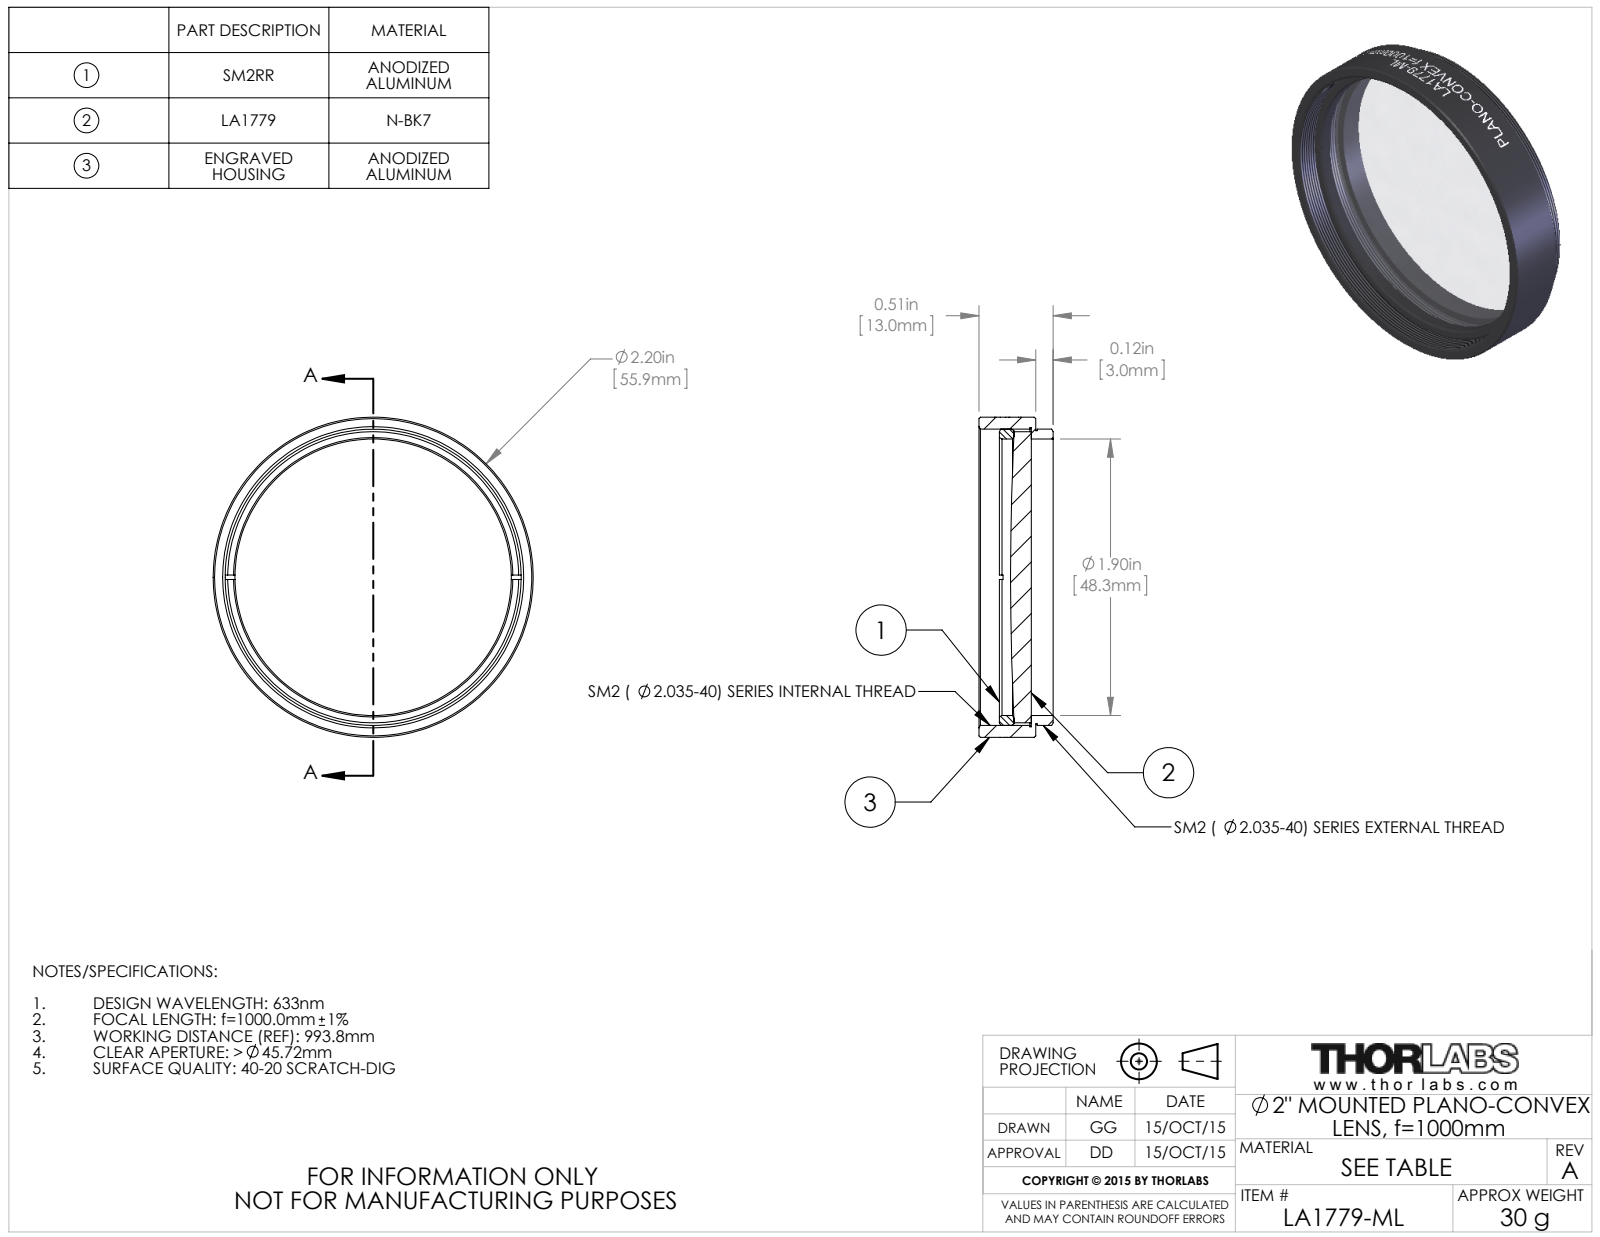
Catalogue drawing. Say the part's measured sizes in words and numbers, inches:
The part is named "TTN039630-E0W". Its 3-D file was written by "SolidWorks 2014 (CONFIG_CONTROL_DESIGN)". It is 3 solids with 110 faces: 16 planar, 74 cylindrical and 20 other. Overall it measures 2.2 by 2.2 by 0.51 inches. Its volume is 0.722 cubic inches and its surface area 17.59 square inches. Round holes: 1 of diameter 1.9, 1 of diameter 2.055. Round bosses or shafts: 1 of diameter 2.2, 1 of diameter 2.035, 1 of diameter 2.015, 1 of diameter 2. The main face-to-face distances are 0.03, 0.39, 0.36, 0.12, 0.15, 0.51, 0.27, 0.15, 0.12, 0.241.
